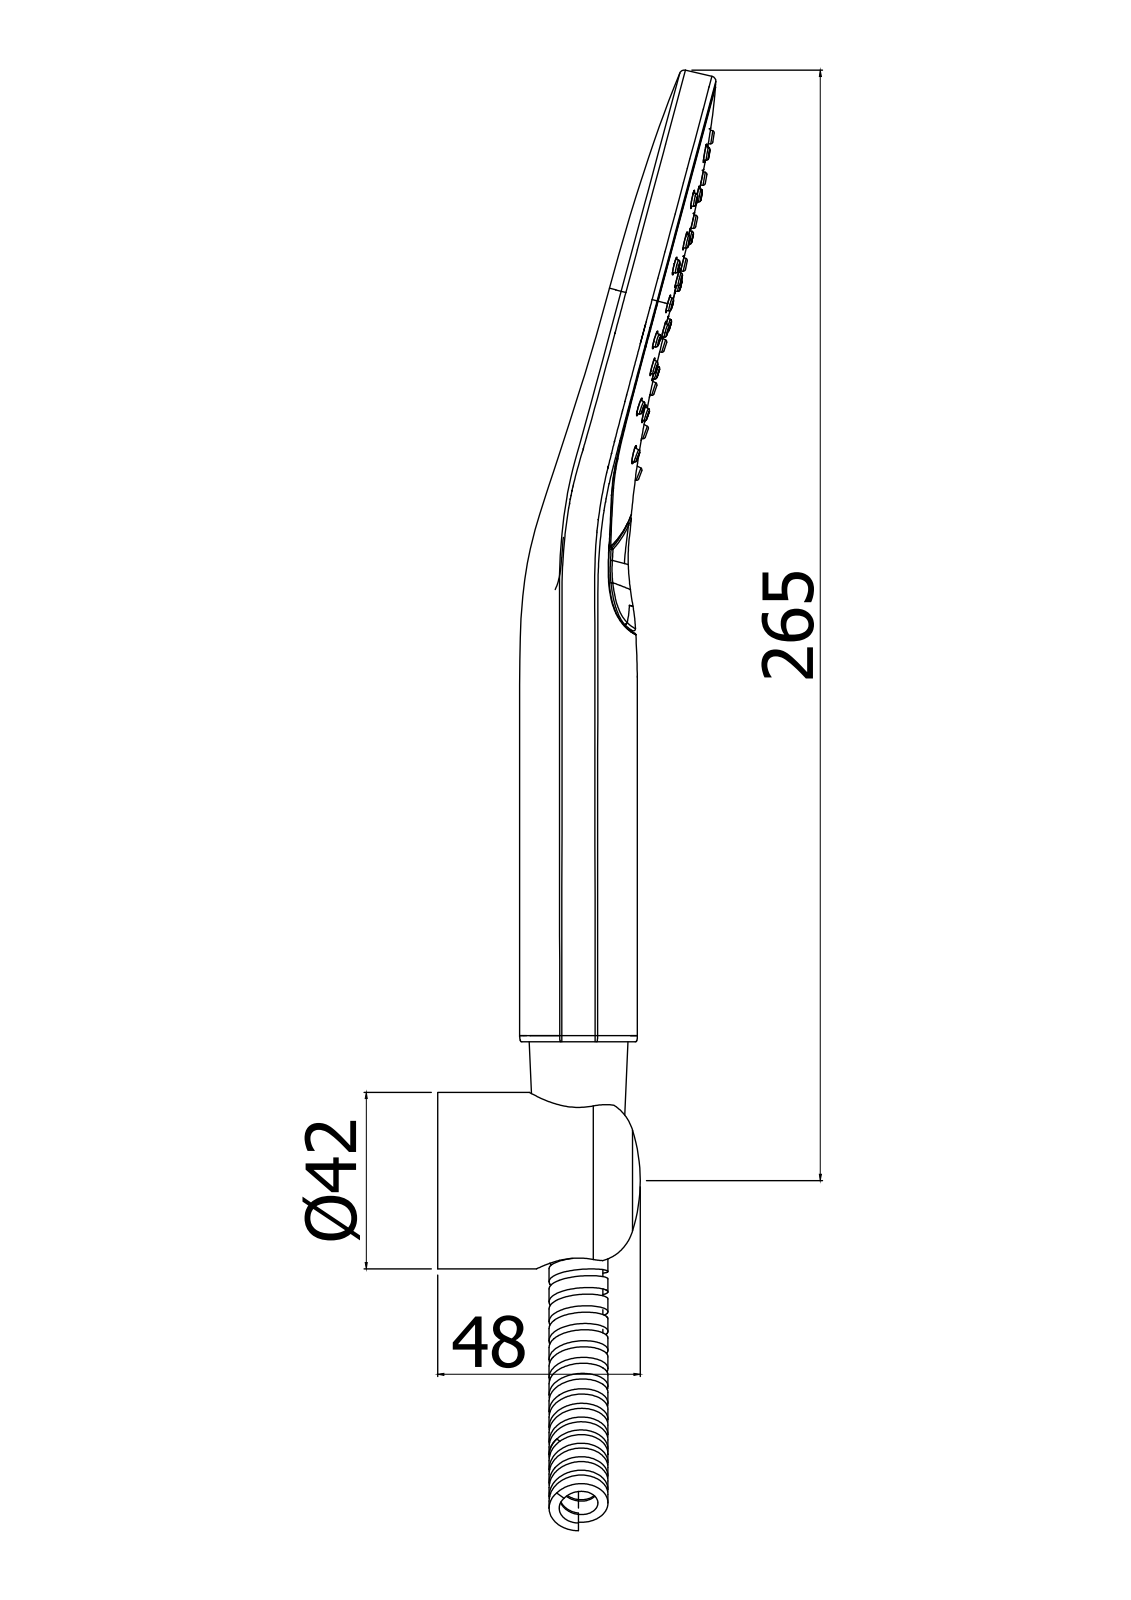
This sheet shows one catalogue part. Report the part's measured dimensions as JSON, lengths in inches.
{"part_name": "4071195CR; 4071021CRDG; 4071084CR_E; 4071084CR_A (+8 more)", "step_written_by": "CREO PARAMETRIC BY PTC INC, 2020044 (CONFIG_CONTROL_DESIGN)", "units": "inches", "bodies": {"solids": 11, "faces": 2710, "planar": 516, "cylindrical": 413, "other": 1781}, "overall_size": [13.68, 4.33, 2.605], "volume_in3": 4.463, "surface_area_in2": 185.8, "round_holes": [[0.236, 4], [0.157, 3], [0.197, 2], [0.315, 2], [0.394, 2], [0.028, 1], [0.106, 1], [0.118, 1], [0.26, 1], [0.37, 1], [0.408, 1], [0.433, 1]], "round_bosses_or_shafts": [[0.276, 4], [0.472, 3], [1.654, 1], [0.976, 1], [0.902, 1], [0.807, 1], [0.734, 1], [0.728, 1]], "partial_cylinders_radius": [[0.008, 44], [0.02, 40], [0.039, 22], [0.012, 21], [0.748, 12], [0.728, 8], [0.059, 5], [0.016, 4]], "face_to_face_distances": [0.079, 0.059, 0.394, 0.728, 0.343, 0.276, 0.807, 0.65, 0.364, 0.327], "hole_center_spacings": [0.354, 0.627, 0.8, 0.979, 1.417, 1.417, 1.473, 1.522]}
